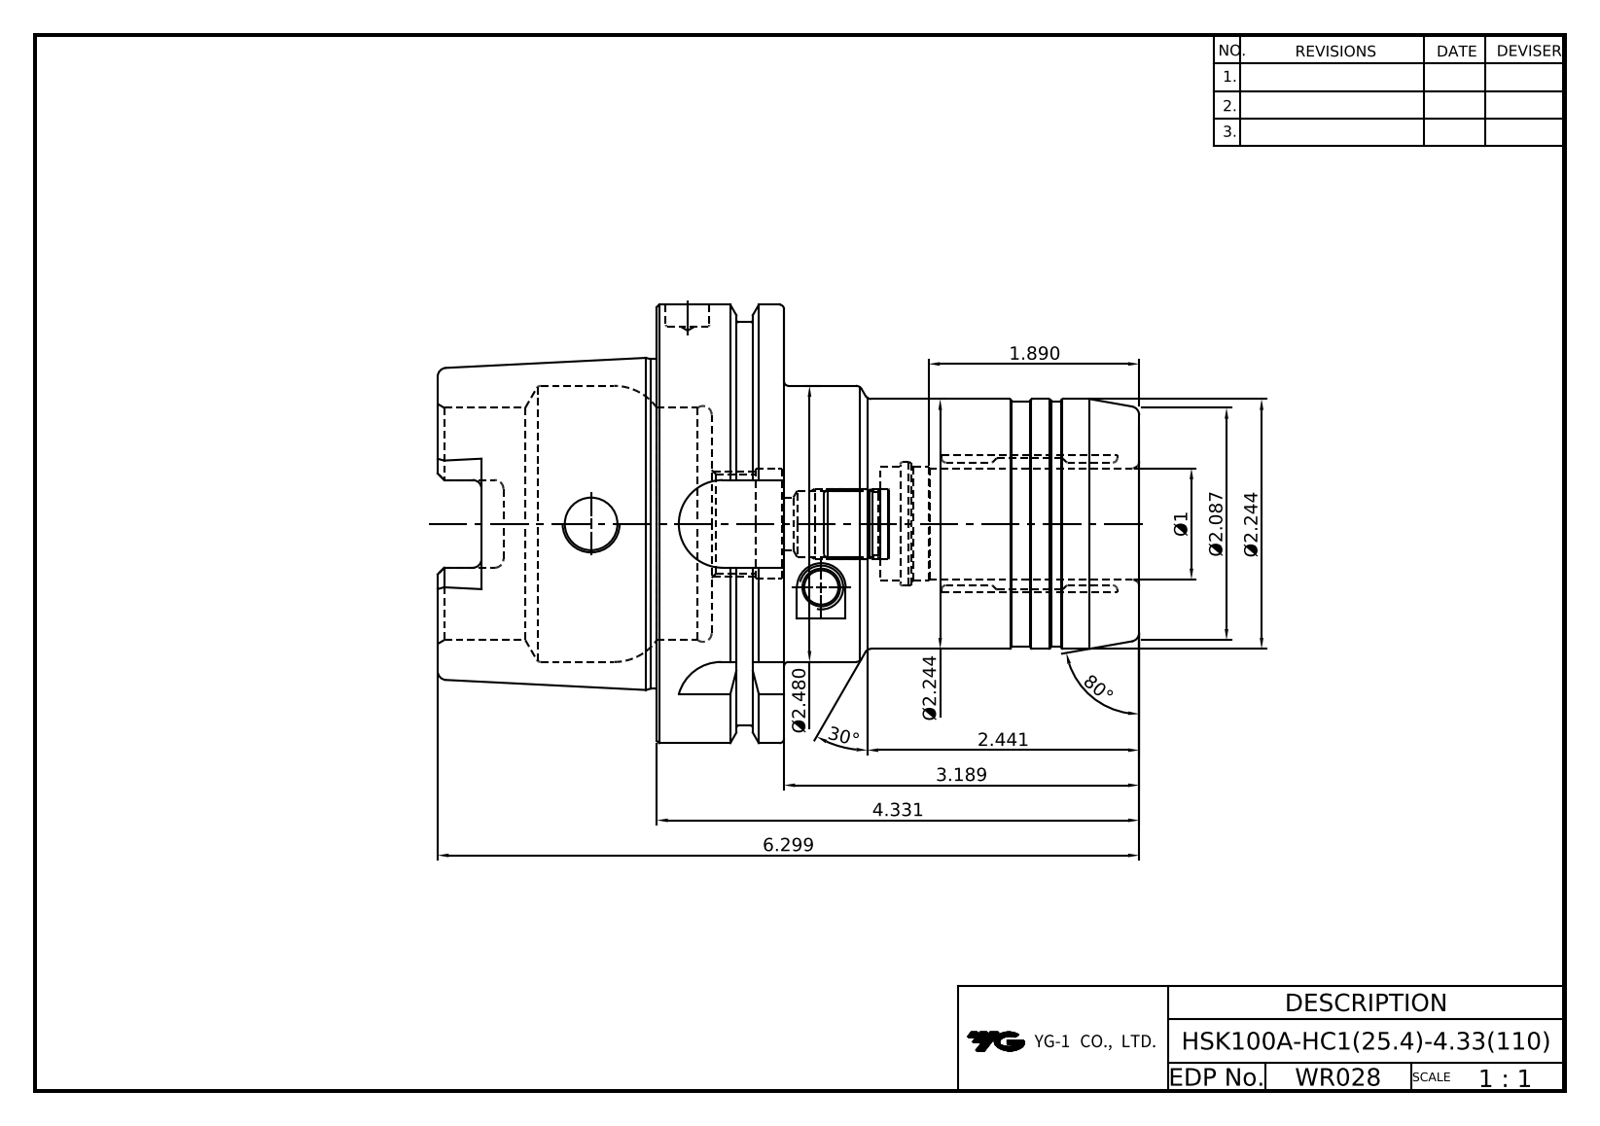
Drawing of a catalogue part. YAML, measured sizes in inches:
part_name: "HSK100A-HC25.4-110"
step_written_by: "Autodesk Inventor 2020 (AUTOMOTIVE_DESIGN)"
units: inches
bodies: {solids: 1, faces: 136, planar: 38, cylindrical: 40, other: 58}
overall_size: [6.299, 3.937, 3.937]
volume: 26.55
surface_area: 107.4
round_holes:
  - {diameter: 0.472, count: 2}
  - {diameter: 0.394, count: 1}
  - {diameter: 0.587, count: 1}
  - {diameter: 0.881, count: 1}
  - {diameter: 0.984, count: 1}
  - {diameter: 1, count: 1}
  - {diameter: 1.016, count: 1}
  - {diameter: 2.087, count: 1}
  - {diameter: 2.48, count: 1}
round_bosses_or_shafts:
  - {diameter: 3.937, count: 1}
  - {diameter: 3.622, count: 1}
  - {diameter: 2.969, count: 1}
  - {diameter: 2.244, count: 1}
  - {diameter: 2.205, count: 1}
partial_cylinders:
  - {radius: 0.079, count: 6}
  - {radius: 0.192, count: 4}
  - {radius: 0.394, count: 4}
face_to_face_distances: [1.142, 0.492, 0.65, 4.331, 3.839, 3.189, 2.461, 1.969, 3.11, 6.299]
